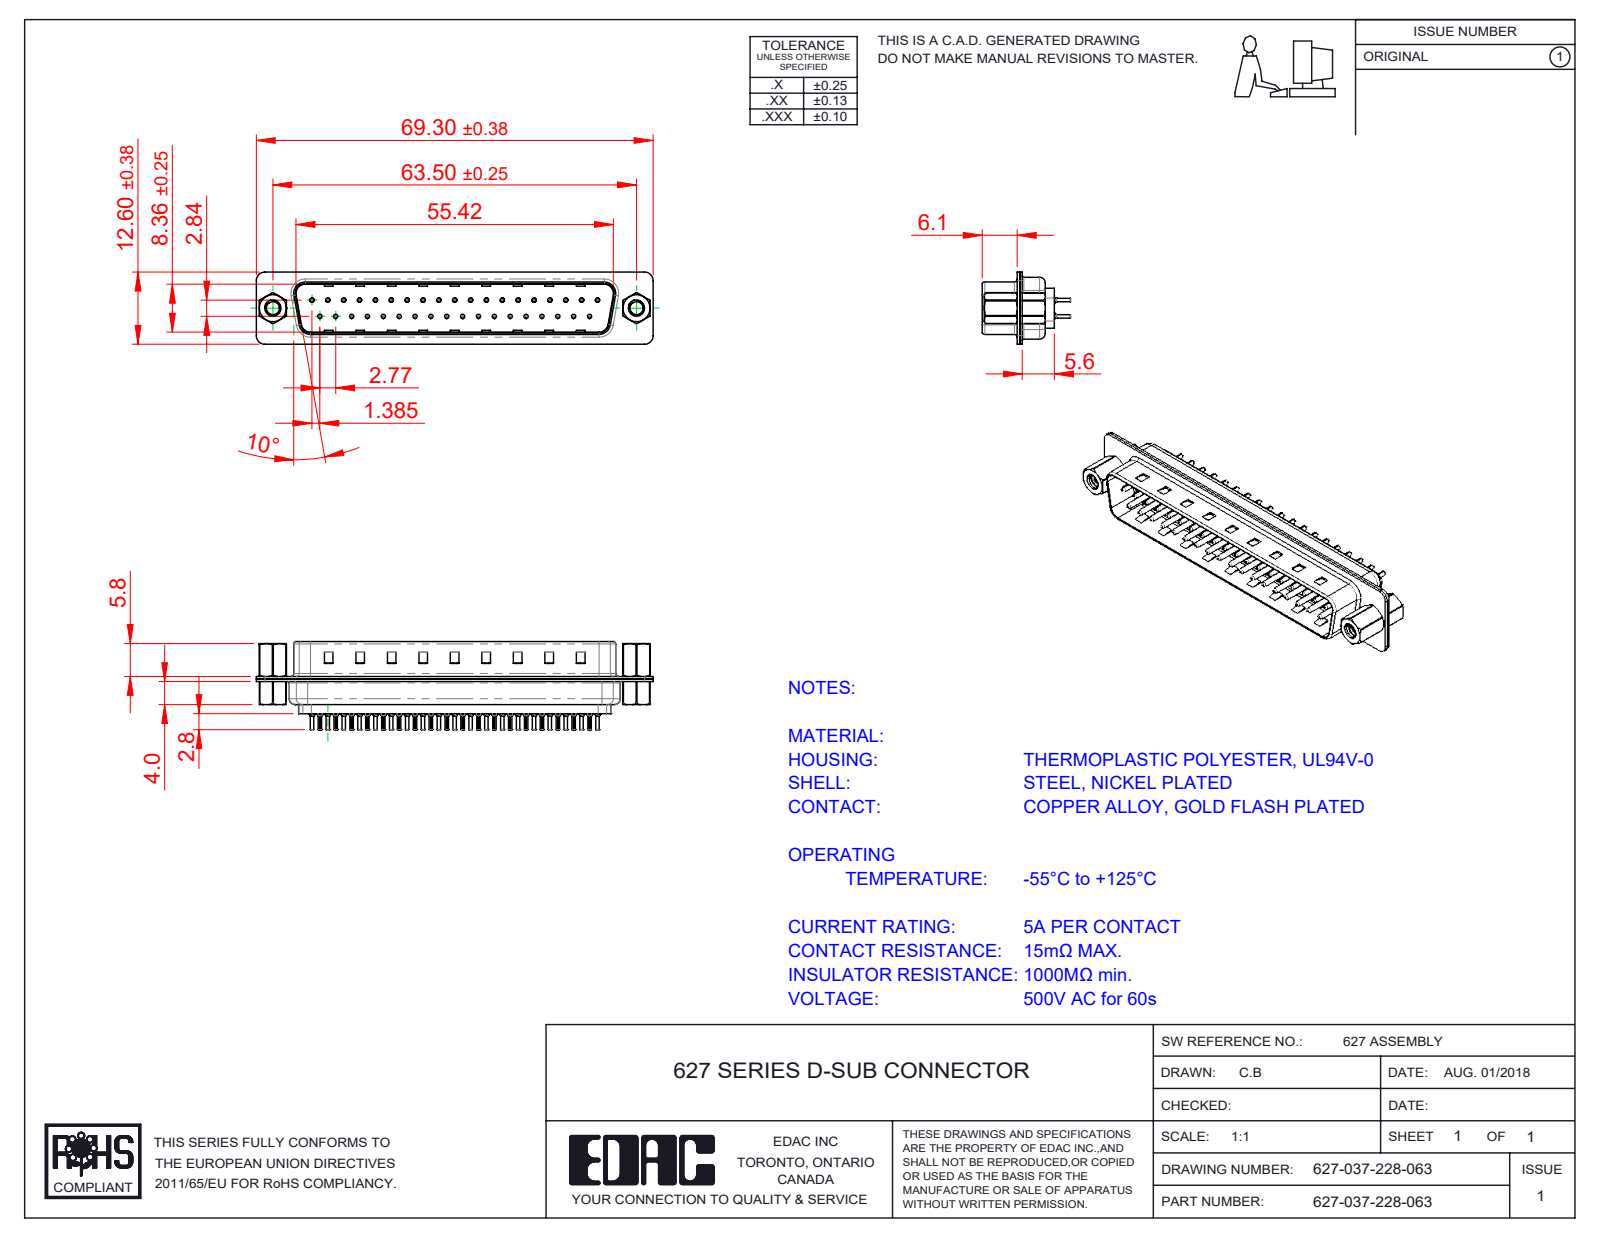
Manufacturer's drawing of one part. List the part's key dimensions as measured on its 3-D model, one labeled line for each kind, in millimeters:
Part name (STEP PRODUCT): 627-037-228-063; 627 Shell Rear_37 Contacts; 627 Contact Row 1_28L; 627 4-40 Hex Standoff (+4 more)
STEP written by: SolidWorks 2020 (CONFIG_CONTROL_DESIGN)
Units: millimetres
Bodies: 45 solids, 4245 faces (1119 planar, 1659 cylindrical, 1467 other)
Overall size (bounding box): 69.3 × 18.8 × 12.6
Volume: 4 764 mm³ · Surface area: 12 768 mm²
Round holes (diameter × count): ⌀0.2 ×37, ⌀0.35 ×37, ⌀1.1 ×37, ⌀1.6 ×37, ⌀2.26 ×2, ⌀2.29 ×2, ⌀4 ×2, ⌀4.8 ×2
Round bosses / shafts (diameter × count): ⌀2 ×37, ⌀1.5 ×37, ⌀0.75 ×37, ⌀0.6 ×37, ⌀5 ×2, ⌀4.9 ×2, ⌀2.79 ×2
Partial cylindrical surfaces — rounded edges, fillets, slot ends (radius × count): R0.1 ×74, R1.5 ×16, R2 ×12, R0.5 ×8, R1.6 ×8, R0.25 ×4, R0.6 ×4, R0.65 ×4
Main face-to-face distances: 0.4, 6.05, 0.82, 9.58, 0.45, 8.4, 0.68, 7.68, 1.5, 1.08
Hole centre spacings: 3.16, 2.77, 5.54, 8.31, 5.04, 10.1, 11.08, 12.78
